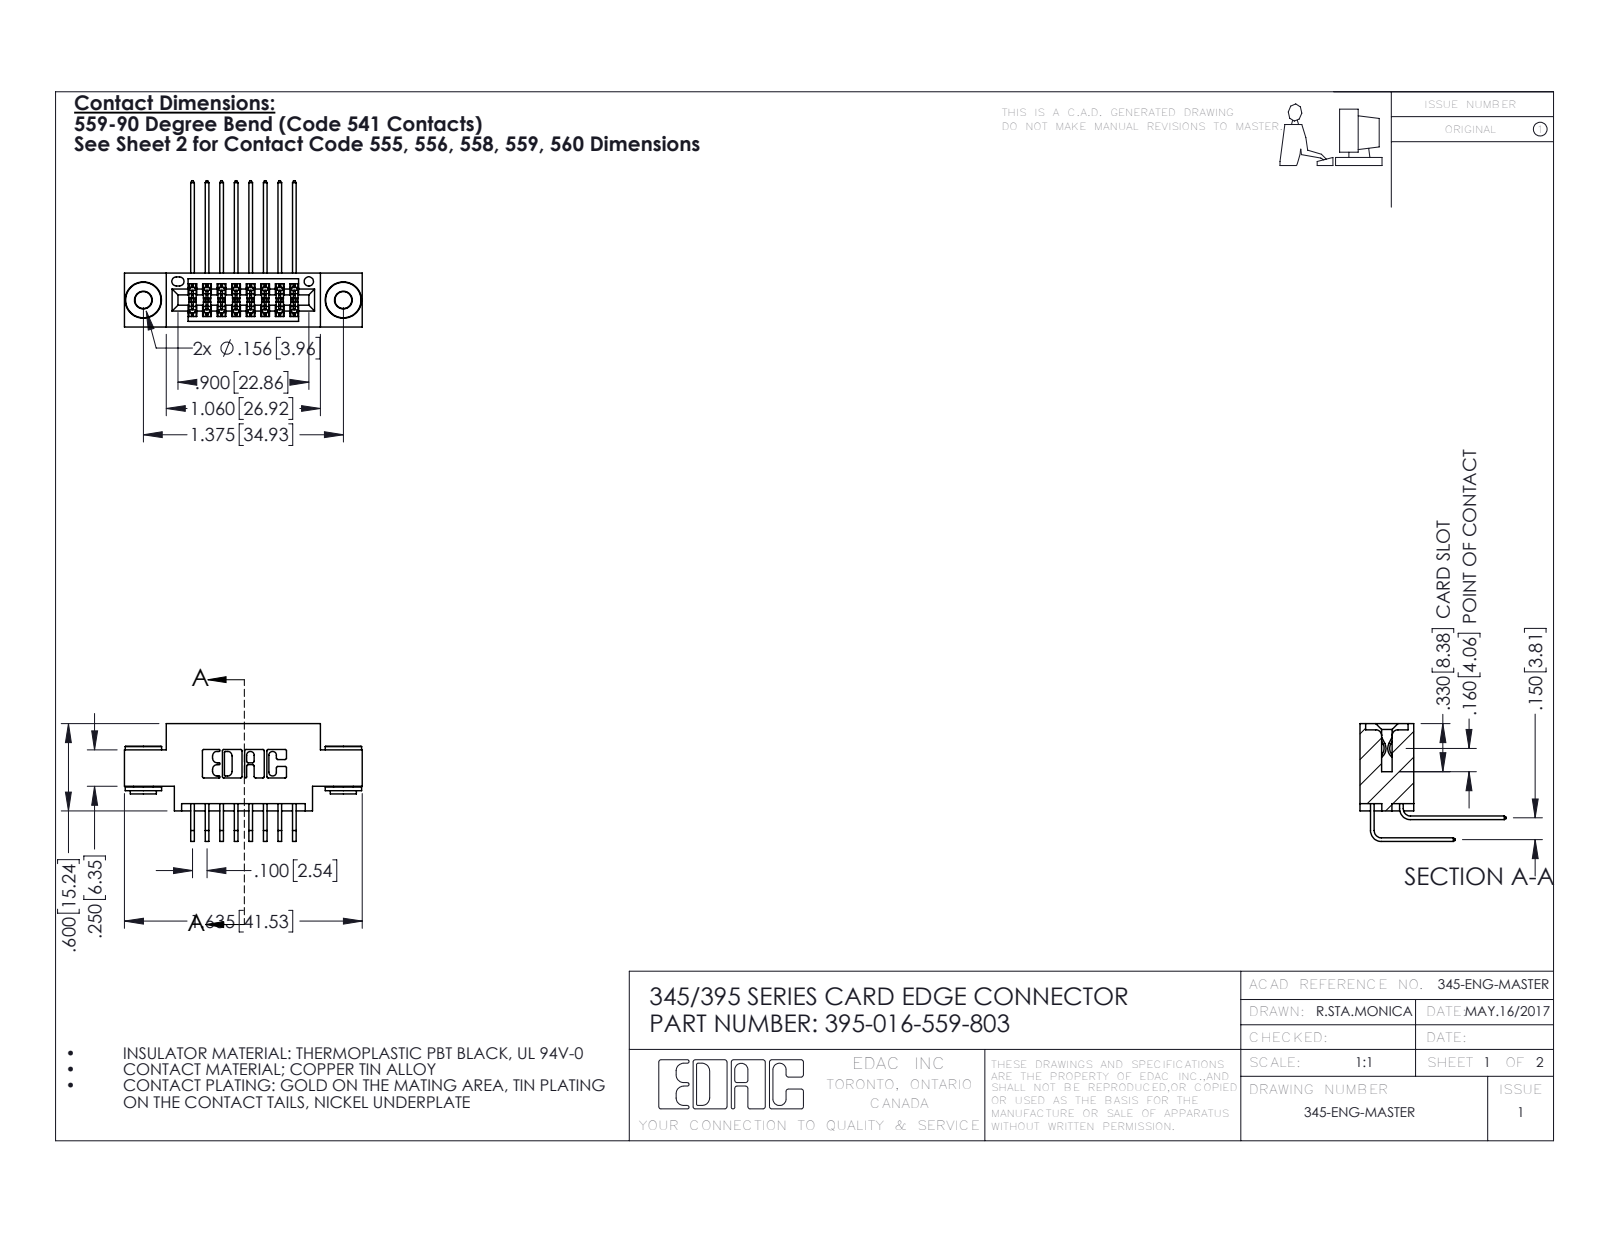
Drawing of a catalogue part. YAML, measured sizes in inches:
part_name: "345-292-001_559 Tail - 2; 345-292-001_558 559 Tail - 1; 345-250-002_345-250-002-102; 395-016-559-803 (+1 more)"
step_written_by: "SolidWorks 2016 (CONFIG_CONTROL_DESIGN)"
units: inches
bodies: {solids: 19, faces: 1000, planar: 654, cylindrical: 338, other: 8}
overall_size: [1.635, 1.005, 0.809]
volume: 0.227
surface_area: 8.708
round_holes:
  - {diameter: 0.116, count: 2}
  - {diameter: 0.156, count: 2}
  - {diameter: 0.064, count: 1}
round_bosses_or_shafts:
  - {diameter: 0.25, count: 2}
  - {diameter: 0.18, count: 2}
  - {diameter: 0.136, count: 2}
partial_cylinders:
  - {radius: 0.006, count: 25}
  - {radius: 0.01, count: 22}
  - {radius: 0.007, count: 6}
  - {radius: 0.031, count: 6}
  - {radius: 0.026, count: 3}
  - {radius: 0.014, count: 2}
  - {radius: 0.019, count: 2}
  - {radius: 0.022, count: 2}
face_to_face_distances: [0.37, 0.2, 0.072, 0.298, 0.1, 0.175, 0.15, 0.098, 0.272, 0.025]
hole_center_spacings: [0.27, 1.144, 1.375]
